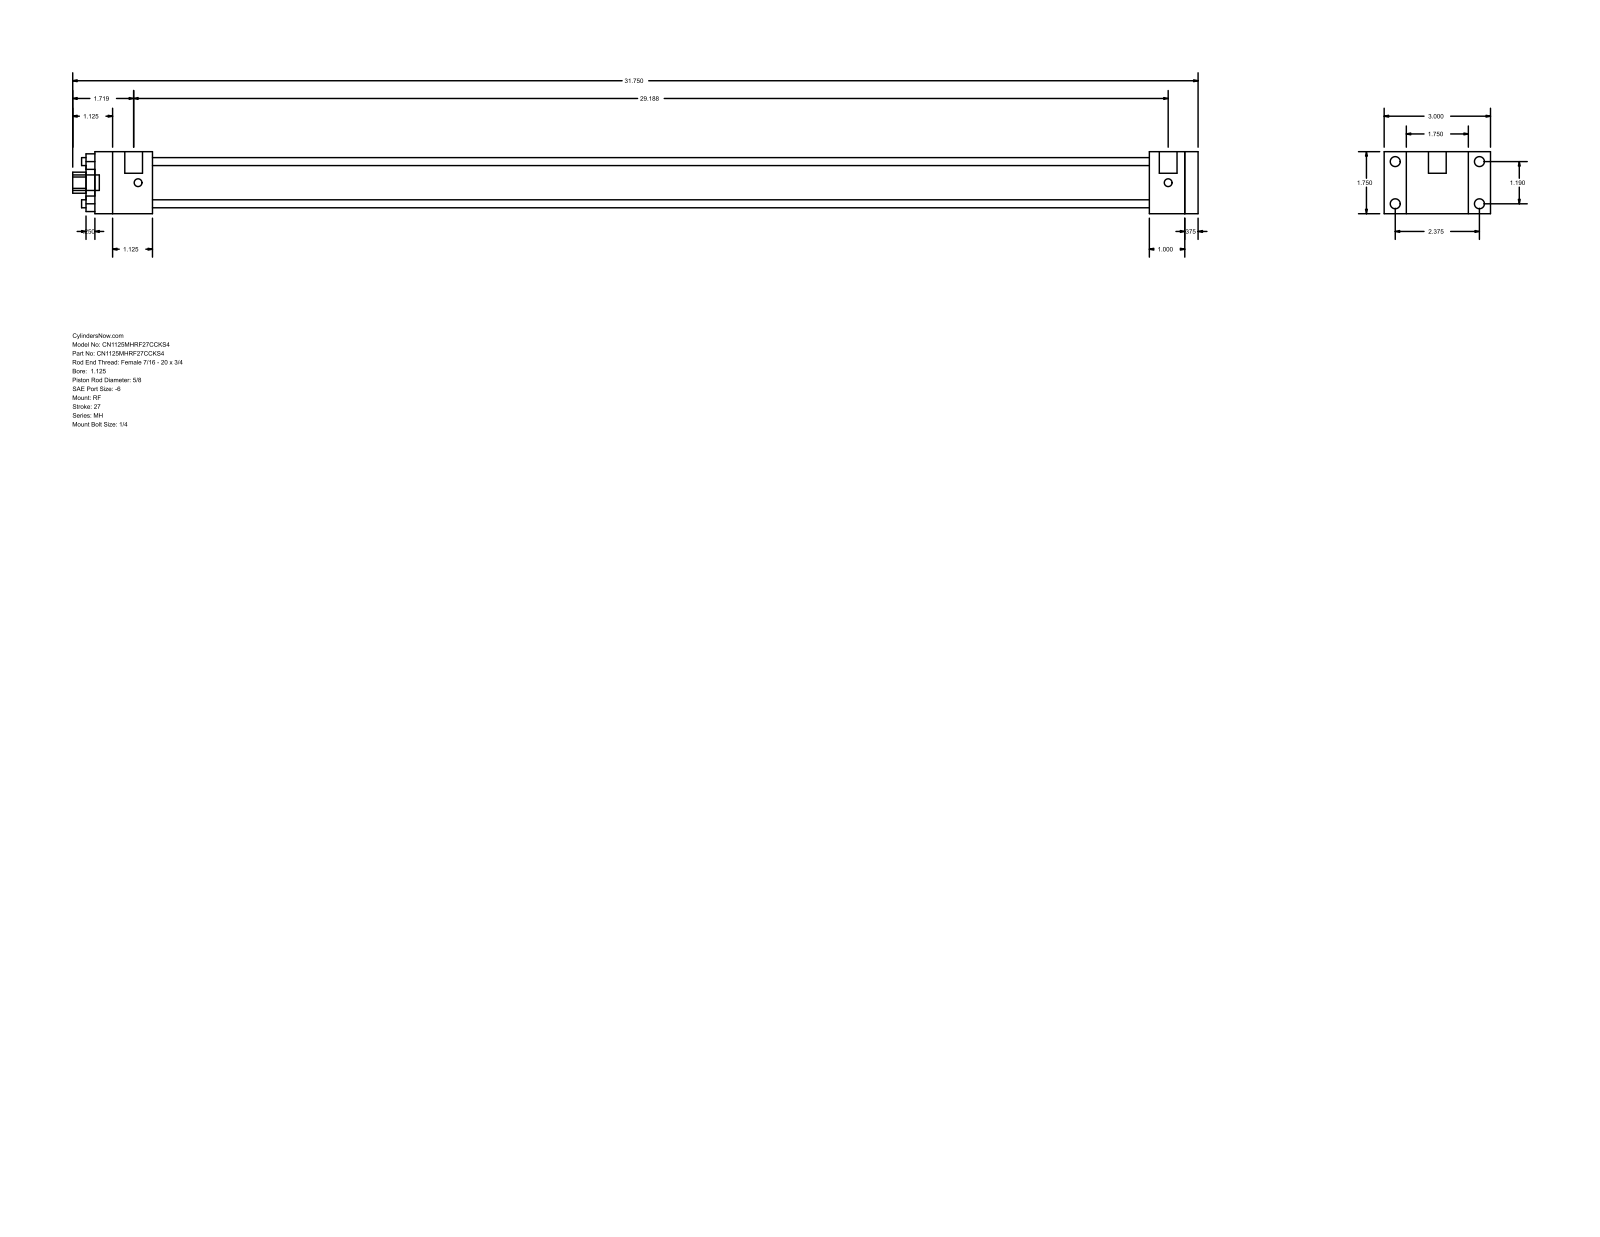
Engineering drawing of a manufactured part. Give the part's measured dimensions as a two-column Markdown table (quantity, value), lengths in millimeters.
| quantity | value |
| --- | --- |
| part name | MH_RF__0112_0.625 |
| STEP written by | GSSL Pune (CONFIG_CONTROL_DESIGN) |
| units | millimeters |
| bodies | 0 solids, 92 faces (64 planar, 28 cylindrical, 0 other) |
| overall size | 806.45 × 76.2 × 44.45 |
| round holes (diameter × count) | 5.71 × 4, 15.88 × 1, 28.57 × 1, 34.92 × 1 |
| round bosses / shafts (diameter × count) | 7.14 × 4, 5.56 × 4, 12.7 × 2, 11.11 × 1 |
| partial cylindrical surfaces (radius × count) | 7.54 × 1 |
| main face-to-face distances | 44.46, 9.53, 790.57, 15.87, 739.77, 749.3, 714.37, 25.4, 34.93, 41.27 |
| hole center spacings | 21.37, 30.22, 42.74 |
